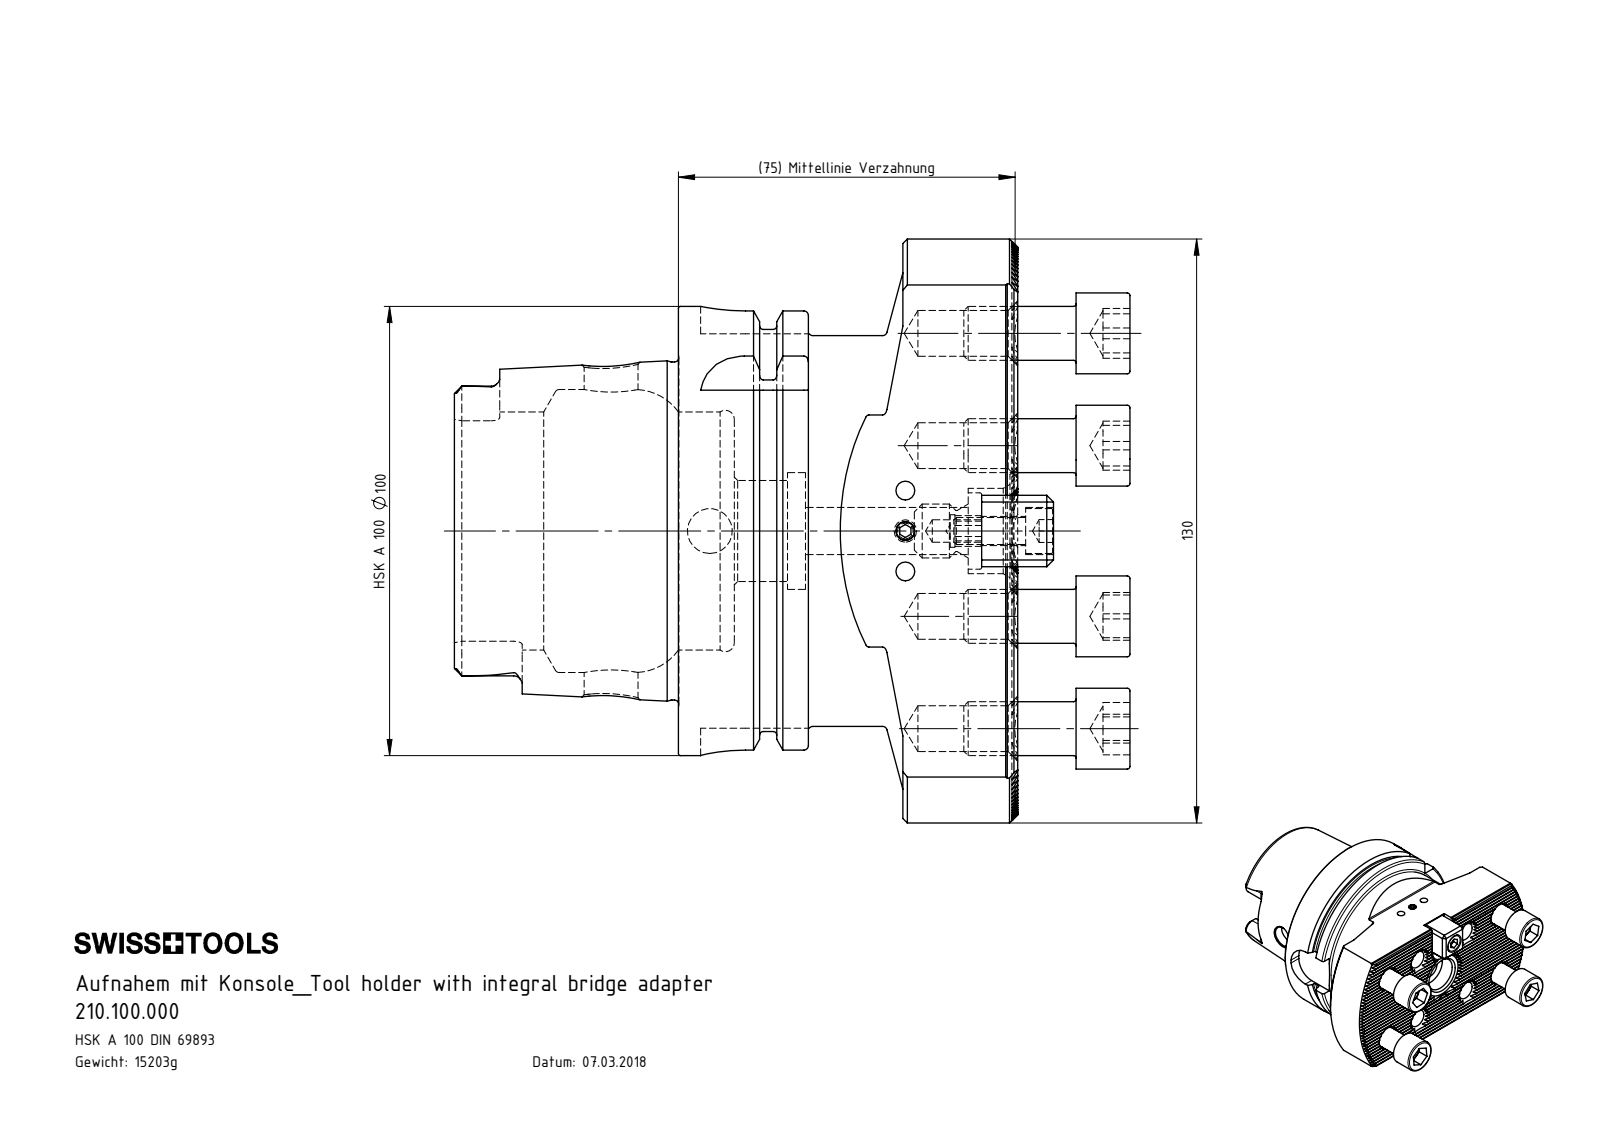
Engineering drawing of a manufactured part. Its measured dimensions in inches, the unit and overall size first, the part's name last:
Units: inches
Overall size (bounding box): 5.924 × 5.118 × 3.937
Round holes (diameter × count): ⌀0.402 ×8, ⌀0.165 ×3, ⌀0.413 ×2, ⌀0.197 ×1, ⌀0.256 ×1, ⌀0.394 ×1, ⌀0.472 ×1, ⌀0.748 ×1, ⌀0.886 ×1, ⌀1.024 ×1, ⌀2.087 ×1, ⌀2.48 ×1
Round bosses / shafts (diameter × count): ⌀0.709 ×4, ⌀0.472 ×4, ⌀3.937 ×1, ⌀3.62 ×1, ⌀3.425 ×1, ⌀2.963 ×1, ⌀0.394 ×1, ⌀0.236 ×1
Partial cylindrical surfaces — rounded edges, fillets, slot ends (radius × count): R0.006 ×34, R0.075 ×6, R0.192 ×4, R0.394 ×4, R0.031 ×2, R0.313 ×1, R2.559 ×1
Main face-to-face distances: 0.068, 0.682, 2.756, 0.341, 0.136, 0.205, 0.273, 0.614, 0.75, 0.137
Hole centre spacings: 0.984, 1.086, 1.575, 1.857, 1.903, 2.48, 2.938, 0.354
Volume: 36.09 in³ · Surface area: 148.2 in²
Bodies: 9 solids, 890 faces (502 planar, 217 cylindrical, 171 other)
Part name (STEP PRODUCT): ISO 4762 - M6 x 16; ISO 4762 - M12 x 25; 210.100.000; HA0-Ko1.K01.075_A_Fertigbearbeitung (+2 more)
STEP written by: SolidWorks 2017 (CONFIG_CONTROL_DESIGN)
